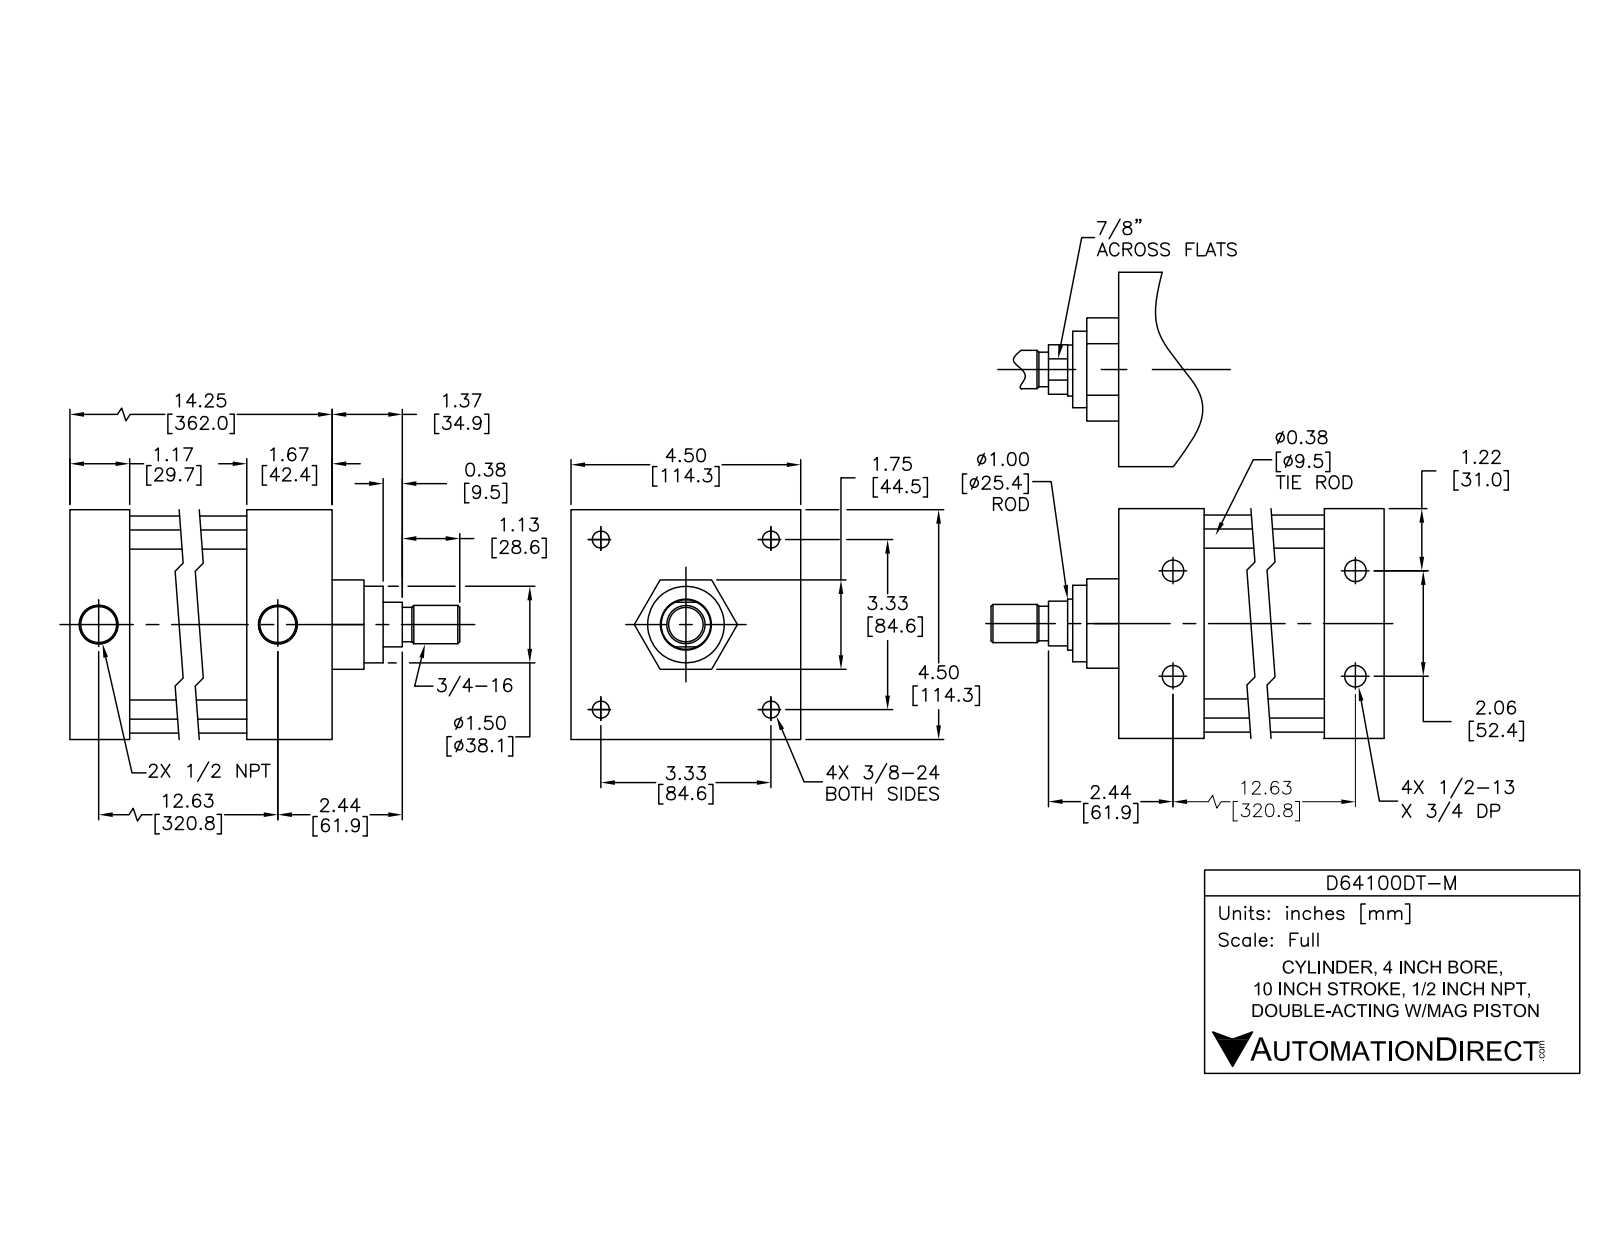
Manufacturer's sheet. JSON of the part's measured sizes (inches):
{"part_name": "D64100DT-M; D64100DT-M PISTON; D64100DT-M BODY", "step_written_by": "SolidWorks 2015 (AUTOMOTIVE_DESIGN)", "units": "inches", "bodies": {"solids": 12, "faces": 303, "planar": 99, "cylindrical": 114, "other": 90}, "overall_size": [16.745, 4.5, 4.5], "volume_in3": 105, "surface_area_in2": 623.6, "round_holes": [[0.33, 4], [0.406, 4], [0.417, 4], [0.625, 4], [0.5, 2], [0.766, 2], [1, 1], [1.003, 1], [4, 1]], "round_bosses_or_shafts": [[0.609, 4], [0.375, 4], [0.34, 4], [4.25, 1], [3.997, 1], [1.75, 1], [0.997, 1], [0.97, 1]], "partial_cylinders_radius": [[0.45, 4]], "face_to_face_distances": [4.5, 0.08, 11.326, 14.246, 1.75, 12.997, 1.249, 11.751, 1.246, 2.495], "hole_center_spacings": [1.031, 12.664, 12.622, 2.062, 2.349, 2.349, 3.322, 3.322]}
